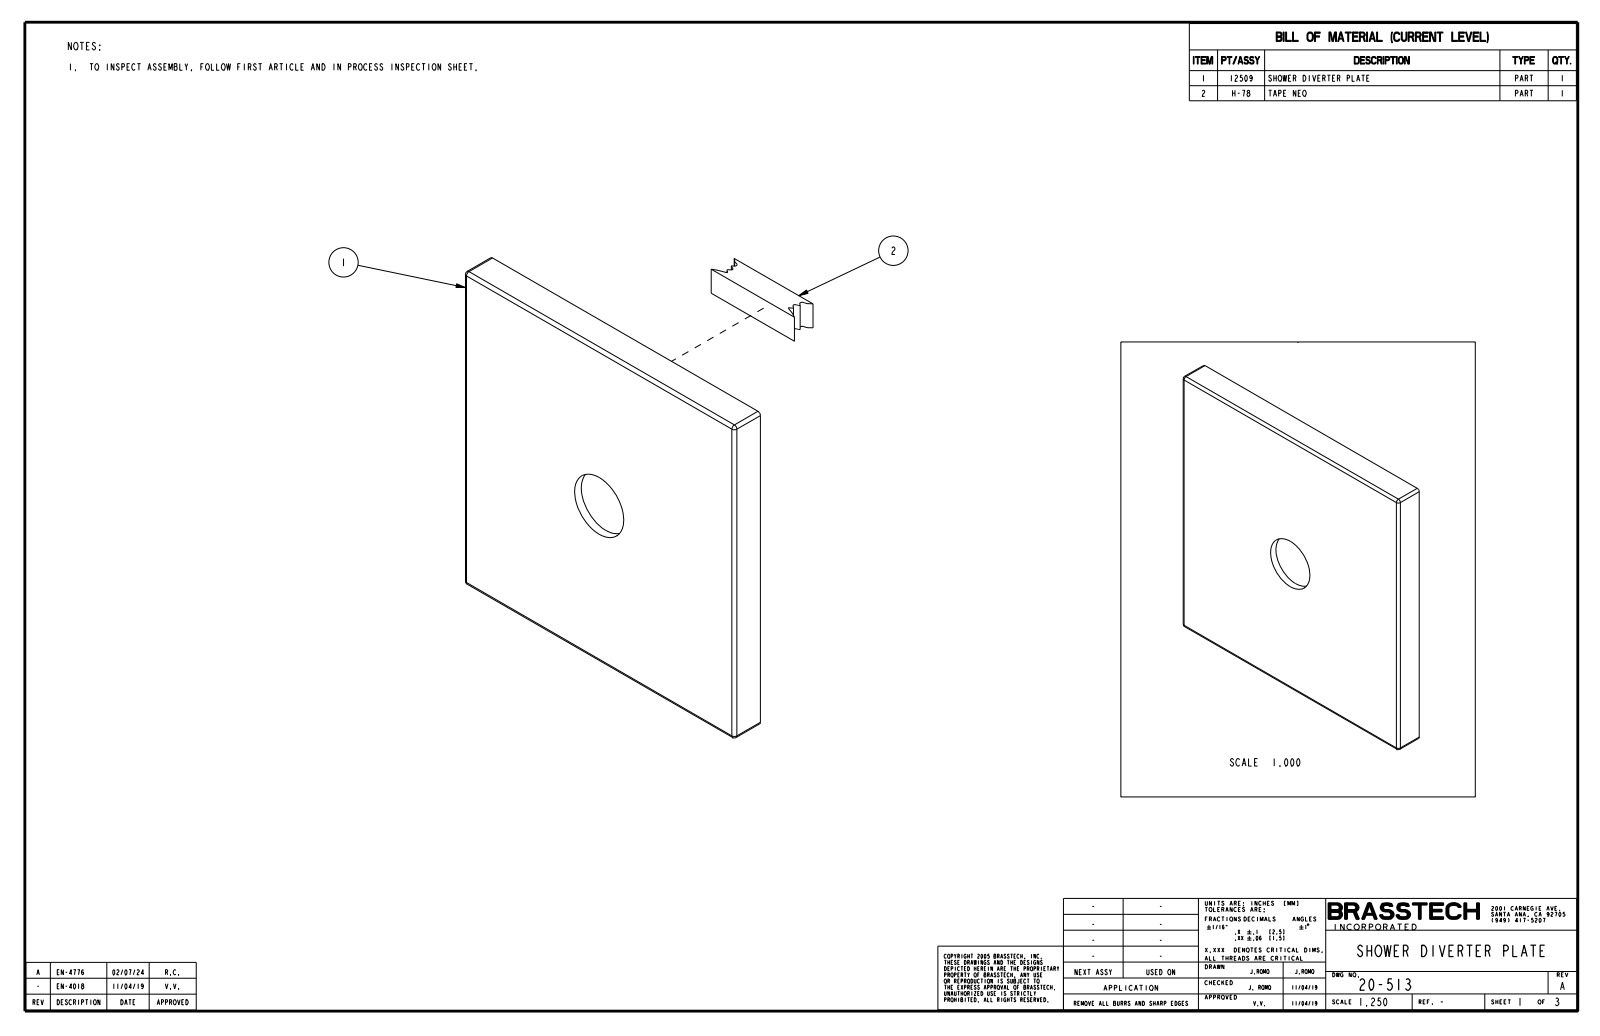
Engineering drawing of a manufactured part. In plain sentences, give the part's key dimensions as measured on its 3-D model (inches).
The part is named "12509; 20-513_ASM". Its 3-D file was written by "CREO PARAMETRIC BY PTC INC, 2023134 (CONFIG_CONTROL_DESIGN)". It is 1 solid with 54 faces: 16 planar, 26 cylindrical and 12 other. Overall it measures 3.25 by 3.25 by 0.313 inches. Its volume is 1.199 cubic inches and its surface area 27.16 square inches. Round holes: 1 of diameter 0.59. Partial cylindrical surfaces (rounded edges, fillets, slot ends): 8 of radius 0.013, 8 of radius 0.03, 8 of radius 0.313. The main face-to-face distances are 0.08, 0.043, 0.123, 3.25, 3.17, 0.19, 0.233, 0.313, 3.09, 0.33.
